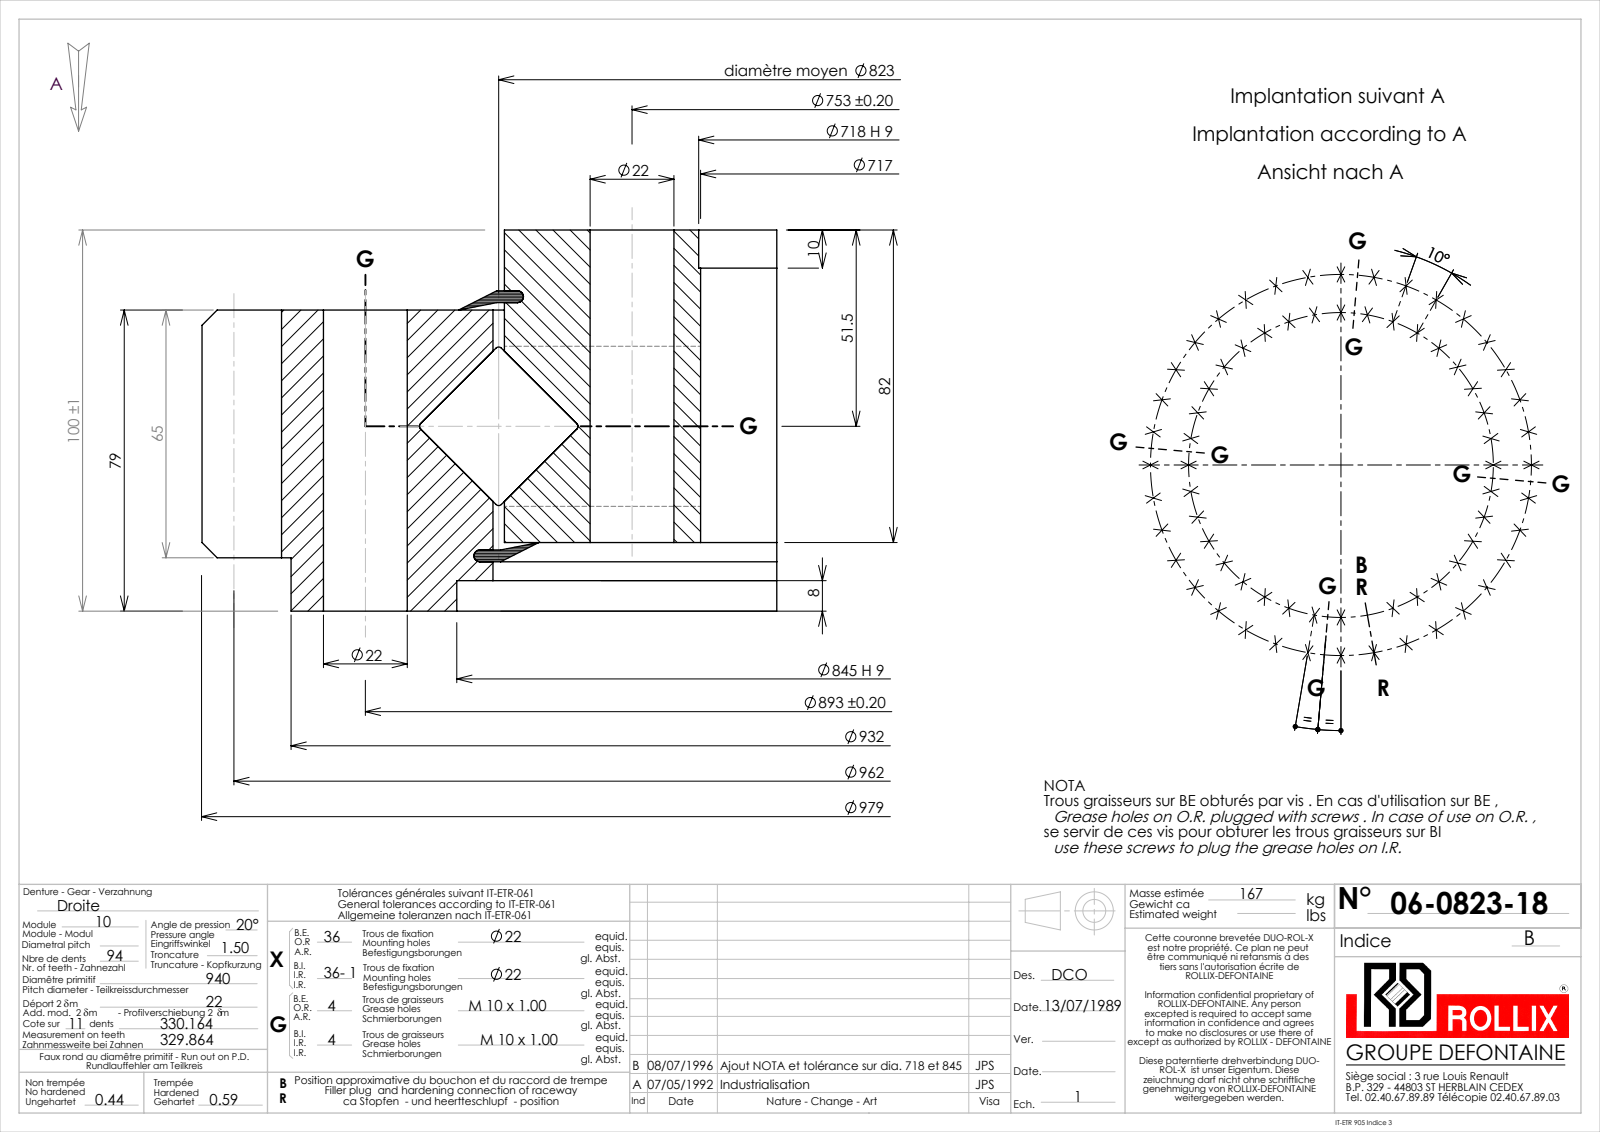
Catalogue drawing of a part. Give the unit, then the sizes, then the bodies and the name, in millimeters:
Units: millimetres
Overall size (bounding box): 979 × 978.75 × 100
Round holes (diameter × count): ⌀22 ×71, ⌀9 ×8, ⌀717 ×1, ⌀718 ×1, ⌀826 ×1, ⌀845 ×1
Round bosses / shafts (diameter × count): ⌀932 ×1, ⌀820 ×1, ⌀30 ×1
Partial cylindrical surfaces — rounded edges, fillets, slot ends (radius × count): R468.5 ×1, R489.5 ×1
Main face-to-face distances: 61, 82, 21, 18, 79, 100, 1.95, 62.95, 5.05, 66.05
Hole centre spacings: 77.83, 377.4, 155.07, 231.13, 305.42, 446.5, 512.2, 574.01
Volume: 20 180 000 mm³ · Surface area: 2 308 000 mm²
Bodies: 5 solids, 814 faces (205 planar, 369 cylindrical, 240 other)
Part name (STEP PRODUCT): 06-0823-18
STEP written by: SolidWorks 2016 (CONFIG_CONTROL_DESIGN)
